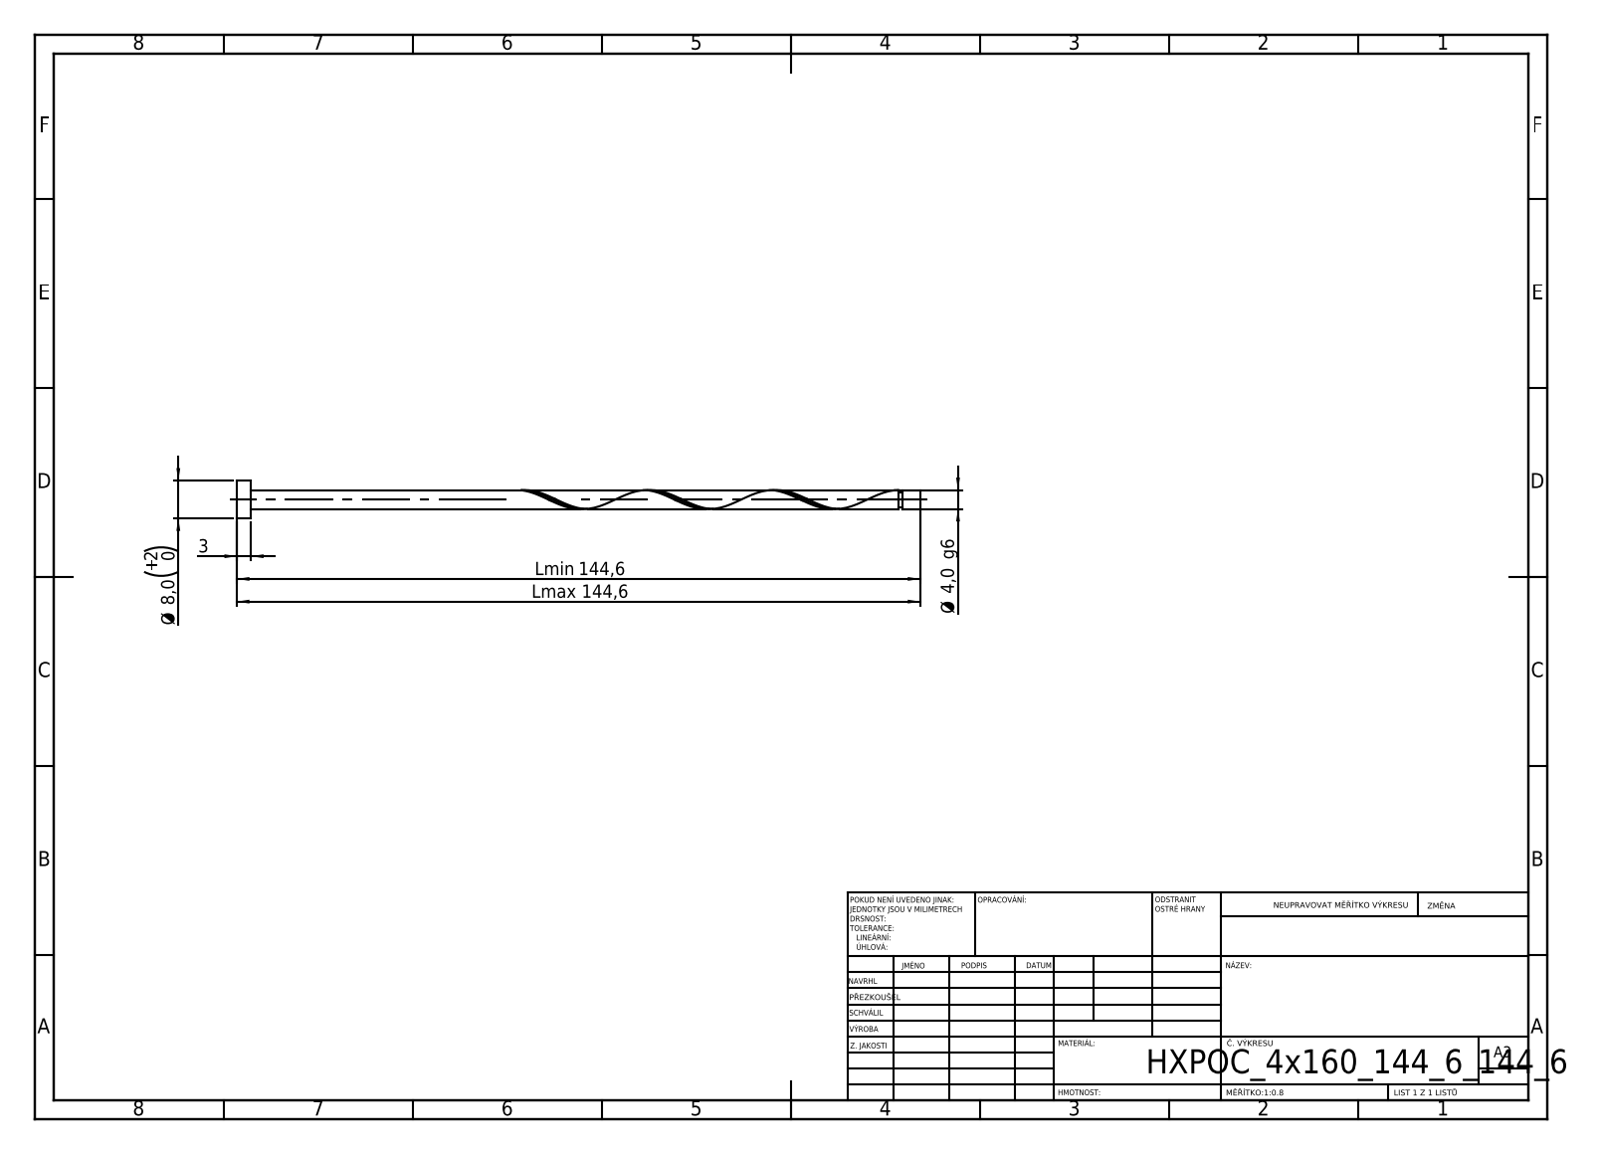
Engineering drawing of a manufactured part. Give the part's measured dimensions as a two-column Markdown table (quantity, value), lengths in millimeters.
| quantity | value |
| --- | --- |
| STEP written by | SolidWorks 2019 (CONFIG_CONTROL_DESIGN) |
| units | millimeters |
| bodies | 1 solid, 21 faces (6 planar, 14 cylindrical, 1 other) |
| overall size | 144.6 × 8 × 8 |
| volume | 1 907 mm³ |
| surface area | 1 997 mm² |
| round bosses / shafts (diameter × count) | 8 × 1, 4 × 1, 3.2 × 1 |
| main face-to-face distances | 3, 144.6, 141.6, 140.87, 137.87, 3.73, 140.07, 137.07, 0.8, 4.53 |
